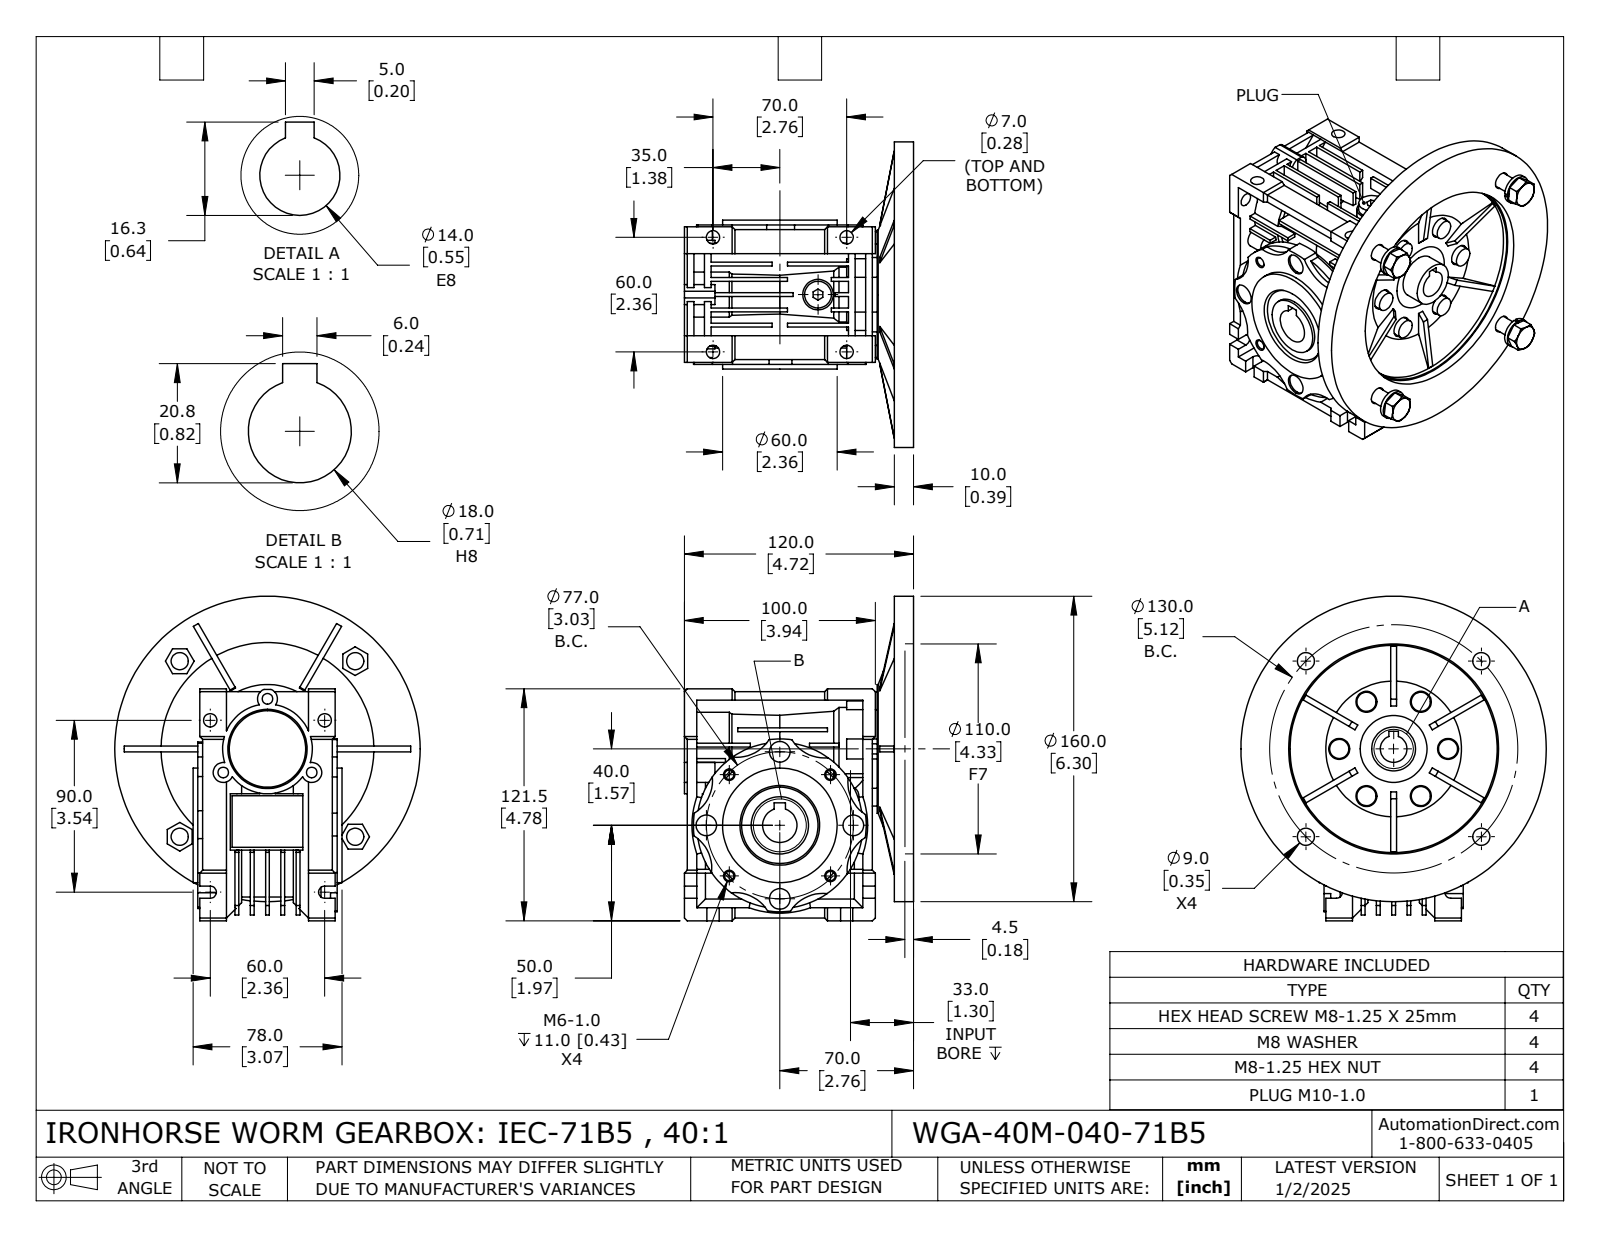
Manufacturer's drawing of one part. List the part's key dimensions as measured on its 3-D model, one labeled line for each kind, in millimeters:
Part name (STEP PRODUCT): WGA-40M-040-71B5
STEP written by: SolidWorks 2024 (CONFIG_CONTROL_DESIGN)
Units: millimetres
Bodies: 18 solids, 1101 faces (630 planar, 290 cylindrical, 181 other)
Overall size (bounding box): 170 × 160 × 137.68
Volume: 780 077 mm³ · Surface area: 202 021 mm²
Round holes (diameter × count): ⌀7 ×6, ⌀11 ×6, ⌀9 ×5, ⌀4.92 ×4, ⌀6.8 ×4, ⌀8 ×4, ⌀8.2 ×4, ⌀10.8 ×4, ⌀5.55 ×3, ⌀14 ×1, ⌀15 ×1, ⌀18 ×1
Round bosses / shafts (diameter × count): ⌀10 ×6, ⌀15.4 ×4, ⌀160 ×1, ⌀75 ×1, ⌀67.5 ×1, ⌀60 ×1, ⌀54 ×1, ⌀47 ×1
Partial cylindrical surfaces — rounded edges, fillets, slot ends (radius × count): R20 ×8, R3.2 ×6, R5.22 ×6, R5.25 ×3, R43.5 ×1, R43.59 ×1, R45.25 ×1, R46 ×1
Main face-to-face distances: 10, 8, 2, 6, 5, 1.5, 16, 24, 14, 2.5
Hole centre spacings: 28.5, 29.1, 70.22, 49.36, 33.54, 37.5, 38.19, 38.5
